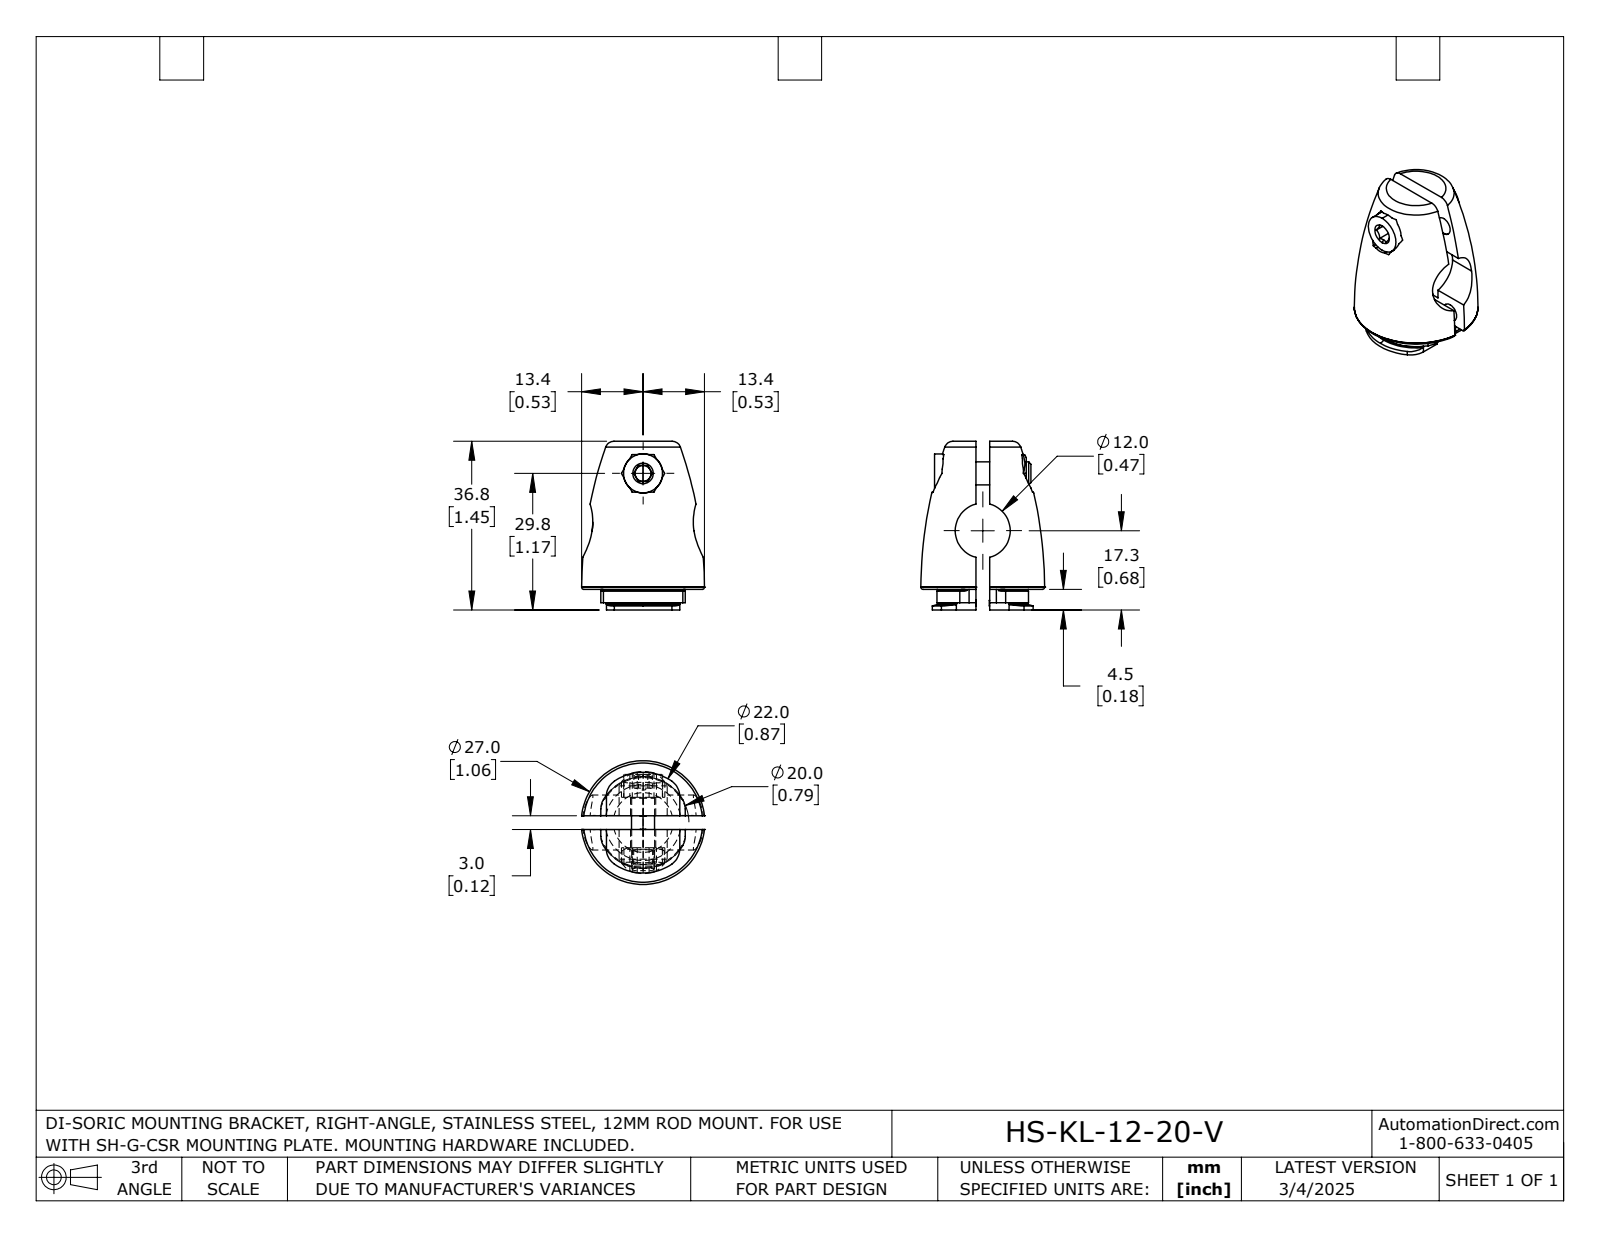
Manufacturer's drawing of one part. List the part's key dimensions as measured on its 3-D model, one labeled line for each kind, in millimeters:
Part name (STEP PRODUCT): HS-KL-12-20-V
STEP written by: SolidWorks 2024 (AUTOMOTIVE_DESIGN)
Units: millimetres
Bodies: 4 solids, 186 faces (80 planar, 70 cylindrical, 36 other)
Overall size (bounding box): 36.8 × 27 × 26.83
Volume: 10 229 mm³ · Surface area: 6 003 mm²
Round holes (diameter × count): ⌀4 ×4, ⌀4.13 ×1, ⌀5.5 ×1, ⌀12 ×1, ⌀16 ×1
Round bosses / shafts (diameter × count): ⌀8.5 ×1, ⌀5 ×1, ⌀1.2 ×1
Partial cylindrical surfaces — rounded edges, fillets, slot ends (radius × count): R4 ×8, R4.3 ×1, R10 ×1, R11 ×1
Main face-to-face distances: 3, 4.5, 4, 7, 3.95, 7.05, 3.05, 36.8, 32.3, 11
Hole centre spacings: 7.01, 22.14, 24.09, 27.24, 14, 18
